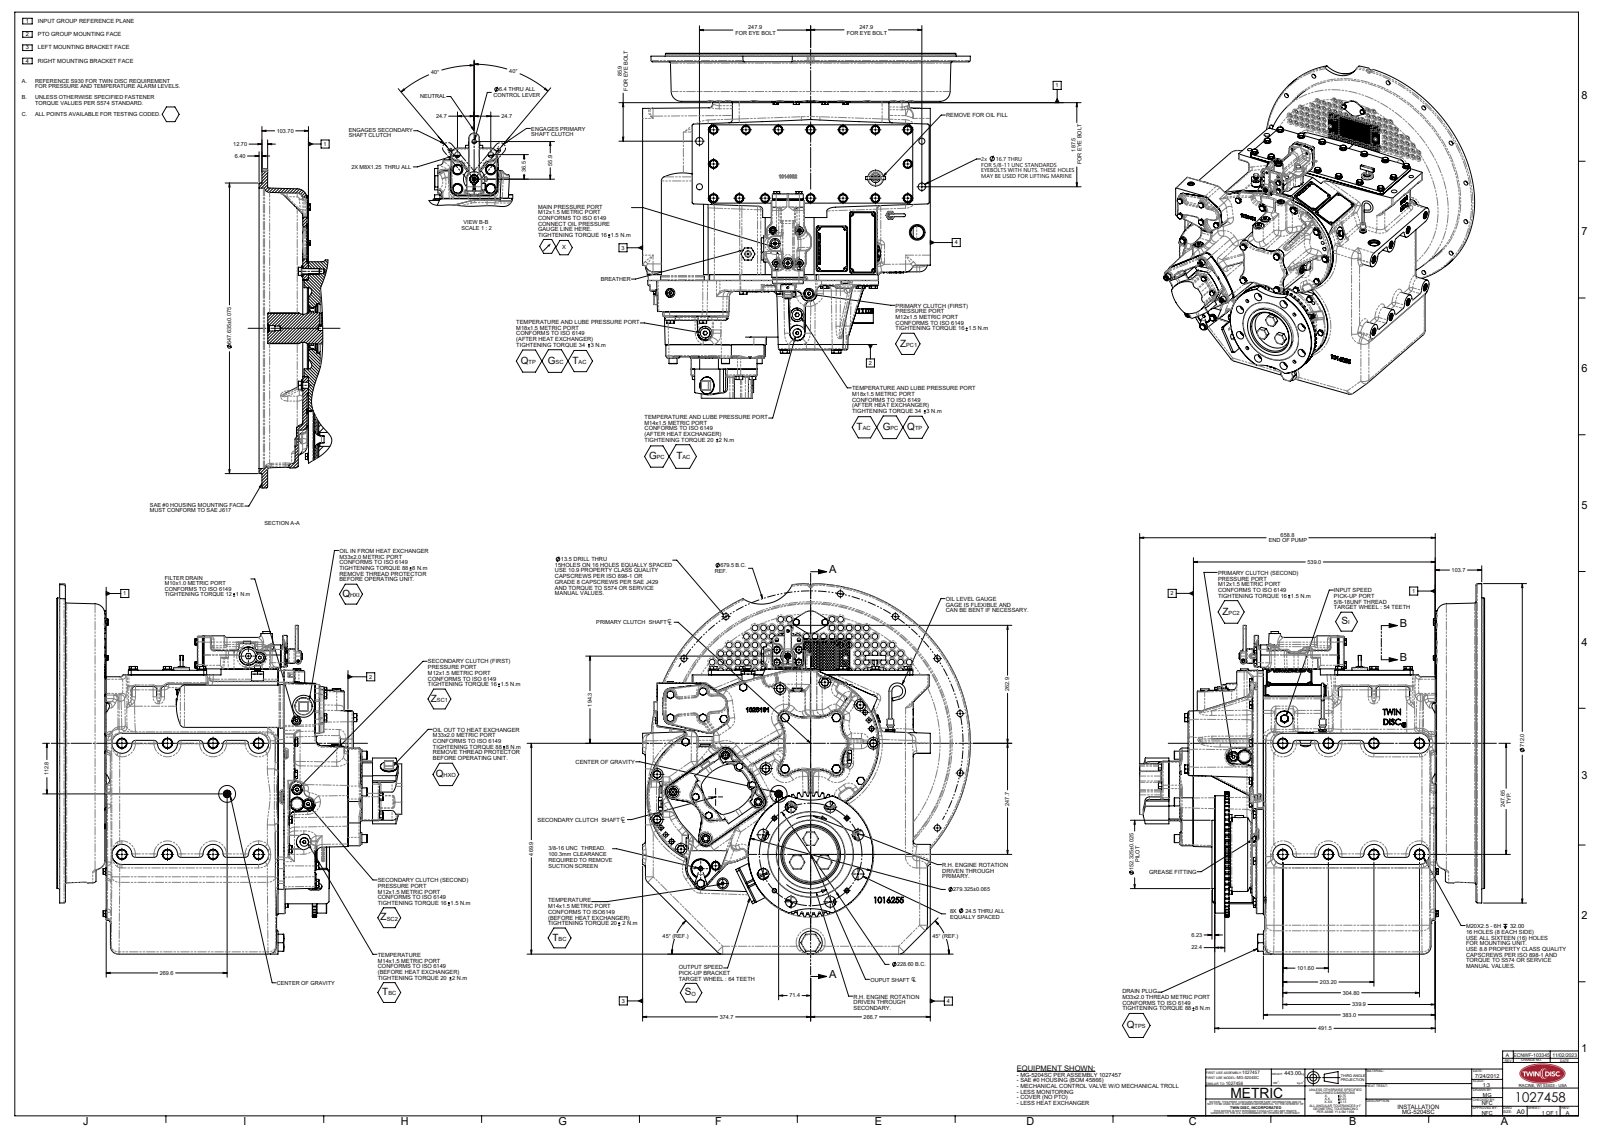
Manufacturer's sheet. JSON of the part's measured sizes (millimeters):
{"part_name": "1027458", "step_written_by": "SolidWorks 2019 (AUTOMOTIVE_DESIGN)", "units": "millimeters", "bodies": {"solids": 0, "faces": 5405, "planar": 1285, "cylindrical": 2036, "other": 2084}, "overall_size": [1005.08, 768.93, 730.69], "round_holes": [[4.5, 273], [12.7, 88], [13.5, 16], [22.82, 8], [24.5, 8], [10, 7], [6.8, 6], [8, 4], [16.5, 4], [6, 3], [11, 2], [16.67, 2]], "round_bosses_or_shafts": [[20, 17], [18, 15], [24, 12], [16.8, 7], [13, 6], [15.32, 4], [18.9, 3], [12.5, 3]], "partial_cylinders_radius": [[46.33, 85], [3, 84], [7.87, 61], [3.05, 55], [12, 48], [1.52, 33], [17.53, 32], [6.4, 28]], "face_to_face_distances": [0.39, 409.21, 408.82, 399.51, 399.12, 9.7, 12.7, 487.12, 13.49, 13.1], "hole_center_spacings": [42.71, 19.1, 27.01, 60.4, 38.2, 68.87, 54.02, 57.3]}
